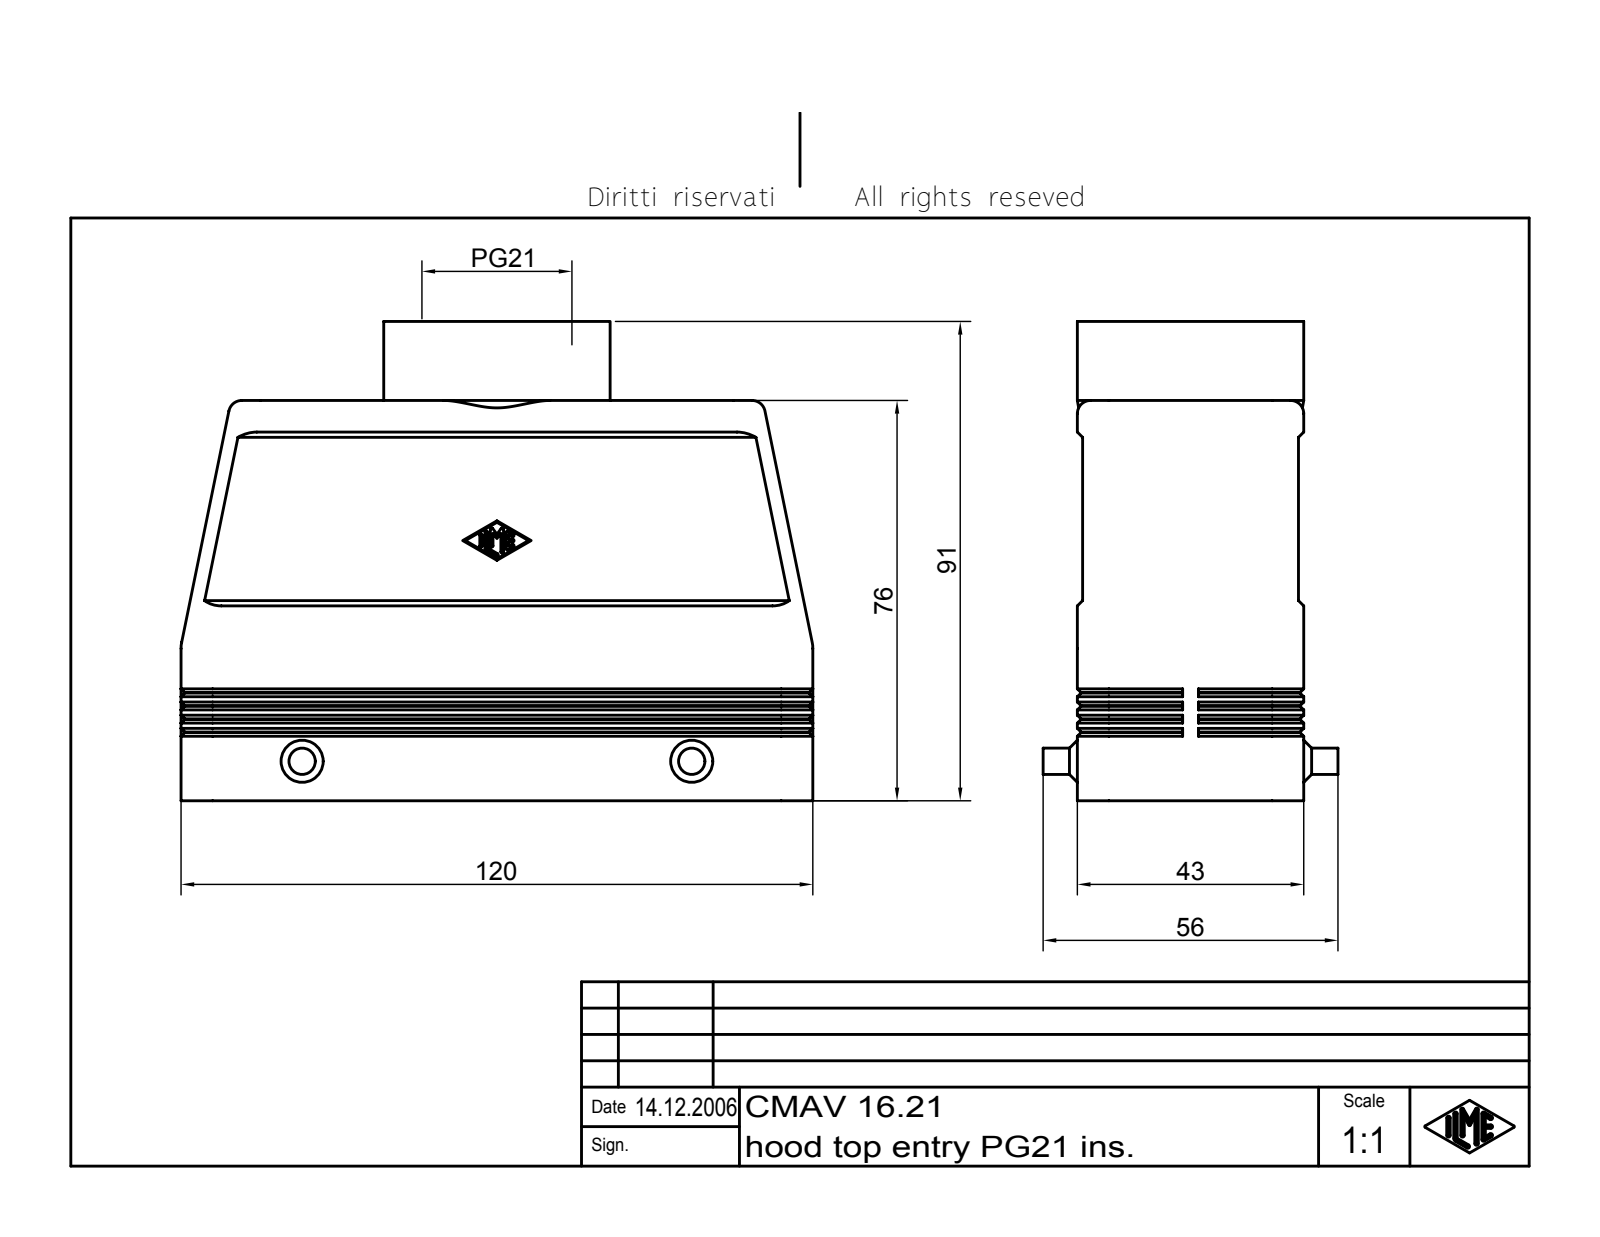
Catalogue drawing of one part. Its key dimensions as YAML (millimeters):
part_name: "CAO Tüllengehäuse 2 Bügel für einen Einsatz"
step_written_by: "Autodesk Inventor 7 (AUTOMOTIVE_DESIGN)"
units: millimeters
bodies: {solids: 1, faces: 413, planar: 153, cylindrical: 108, other: 152}
overall_size: [120, 91, 56]
volume: 96956
surface_area: 57164
round_holes:
  - {diameter: 24.78, count: 1}
  - {diameter: 26.78, count: 1}
round_bosses_or_shafts:
  - {diameter: 5, count: 2}
  - {diameter: 43, count: 1}
  - {diameter: 25.78, count: 1}
partial_cylinders:
  - {radius: 0.25, count: 14}
  - {radius: 6, count: 10}
  - {radius: 2, count: 4}
  - {radius: 2.5, count: 4}
  - {radius: 3, count: 4}
  - {radius: 5.3, count: 2}
face_to_face_distances: [3, 37, 40, 1, 2, 42, 39, 43, 41, 12]
